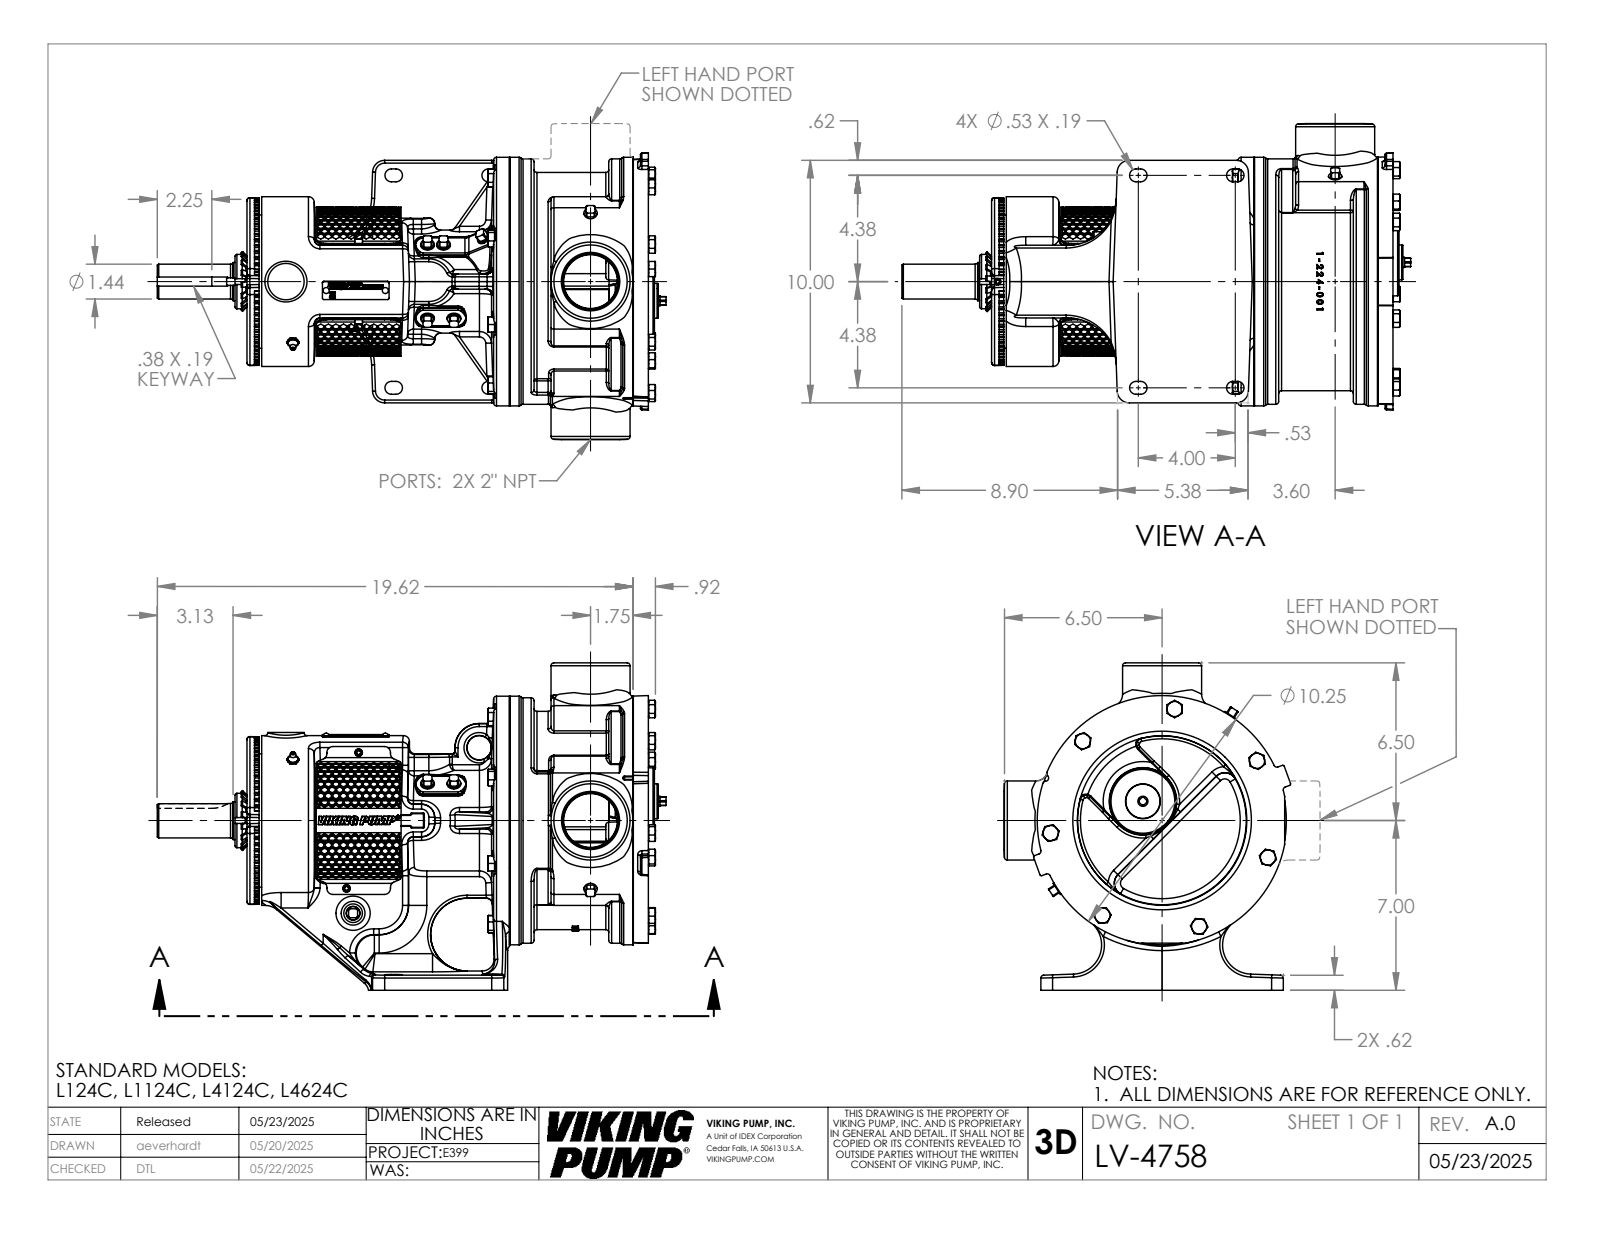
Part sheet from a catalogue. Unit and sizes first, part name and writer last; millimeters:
Units: millimetres
Overall size (bounding box): 533 × 342.9 × 300.2
Round holes (diameter × count): ⌀27.8 ×8, ⌀5.1 ×6, ⌀6.4 ×6, ⌀4 ×3, ⌀6.8 ×2, ⌀8 ×2, ⌀11.5 ×1, ⌀40.1 ×1, ⌀40.5 ×1, ⌀46.5 ×1, ⌀62 ×1, ⌀133.4 ×1
Round bosses / shafts (diameter × count): ⌀15.9 ×12, ⌀15.9 ×3, ⌀11.1 ×3, ⌀7.9 ×3, ⌀82.8 ×2, ⌀260.4 ×1, ⌀257 ×1, ⌀177.8 ×1
Partial cylindrical surfaces — rounded edges, fillets, slot ends (radius × count): R1.6 ×109, R3 ×86, R1.8 ×74, R6.1 ×48, R1.5 ×15, R6.4 ×14, R12.7 ×12, R19.1 ×12
Main face-to-face distances: 350.7, 89.8, 260.9, 12.7, 57.2, 54.4, 144.3, 405.1, 15.4, 69.9
Hole centre spacings: 76.2, 34.9, 55.4, 91.7, 112.9, 117.5, 162.7, 166.1
Volume: 12 300 000 mm³ · Surface area: 736 100 mm²
Bodies: 1 solid, 4036 faces (1314 planar, 818 cylindrical, 1904 other)
Part name (STEP PRODUCT): LV-4758
STEP written by: SolidWorks 2024 (AUTOMOTIVE_DESIGN)
